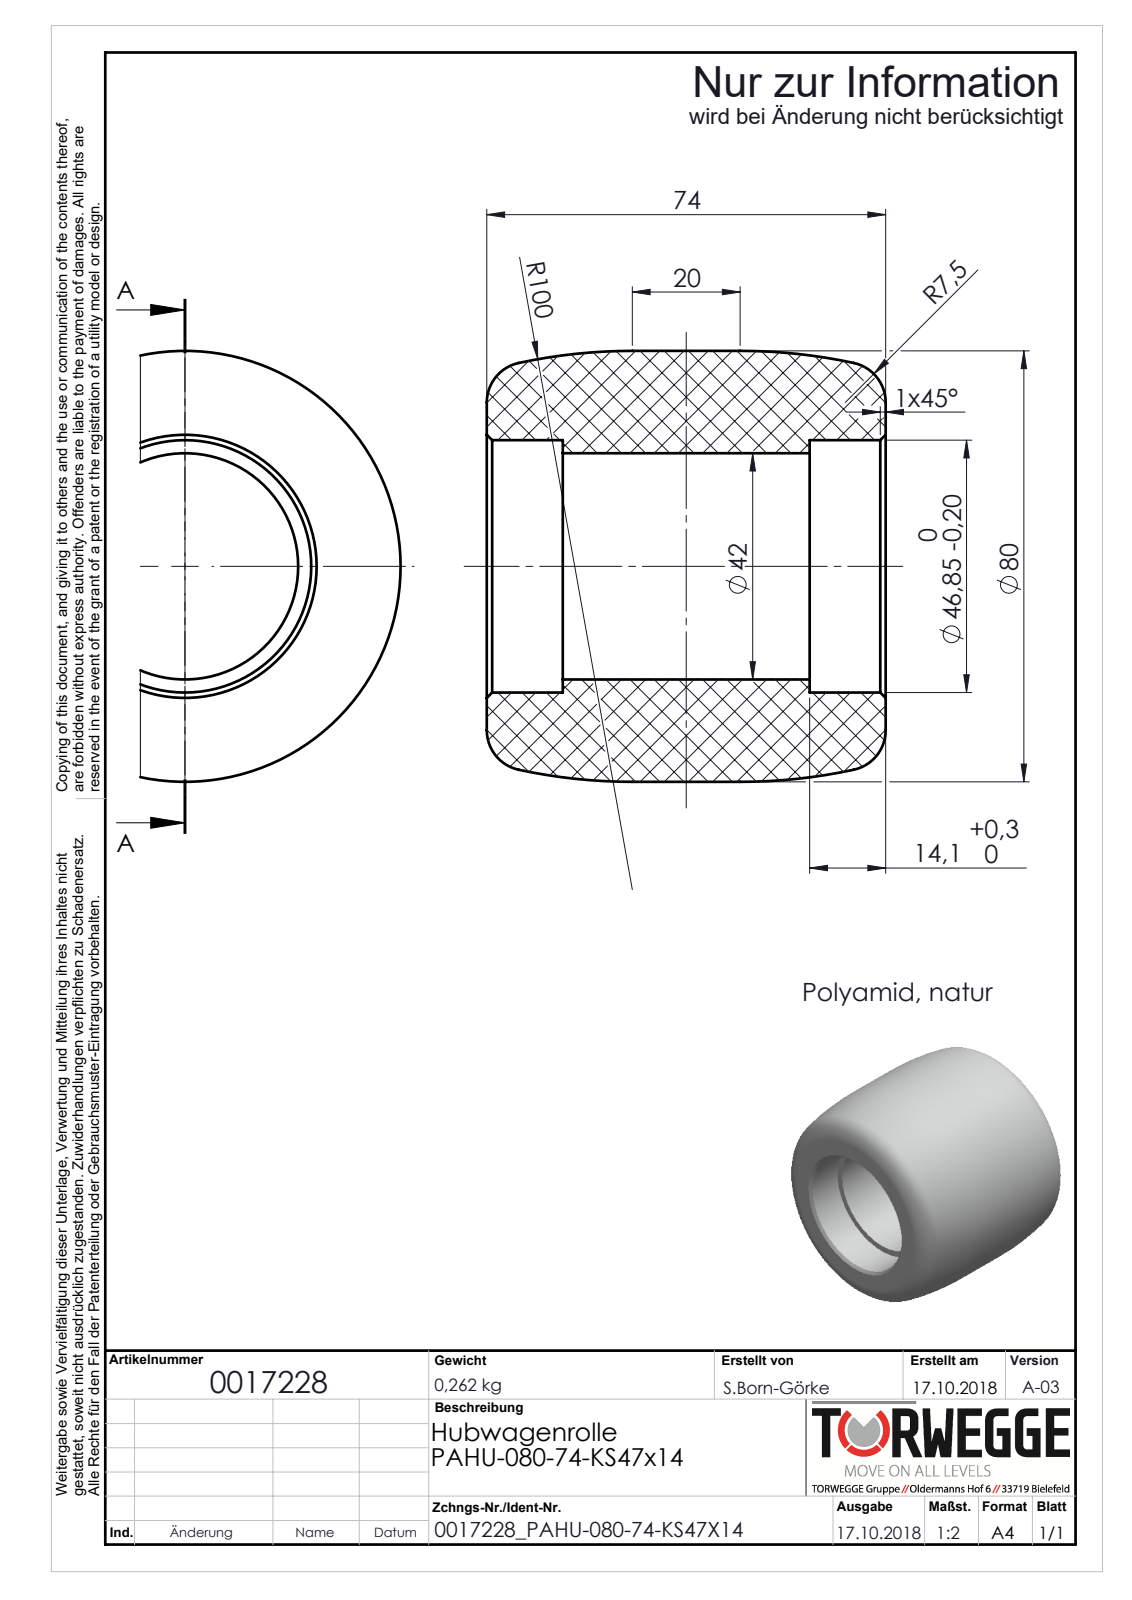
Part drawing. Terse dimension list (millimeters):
name: 0017228_PAHU-080-74-KS47x14
written by: SolidWorks 2018 (AUTOMOTIVE_DESIGN)
unit: mm
bodies: 1 solid, 14 faces (4 planar, 4 cylindrical, 6 other)
size: 80 × 80 × 74
volume: 240 499 mm³; area: 33 023 mm²
holes: 1× ⌀42, 1× ⌀46.85
bosses: 1× ⌀80
face distances: 74, 14.1, 59.9, 45.8
